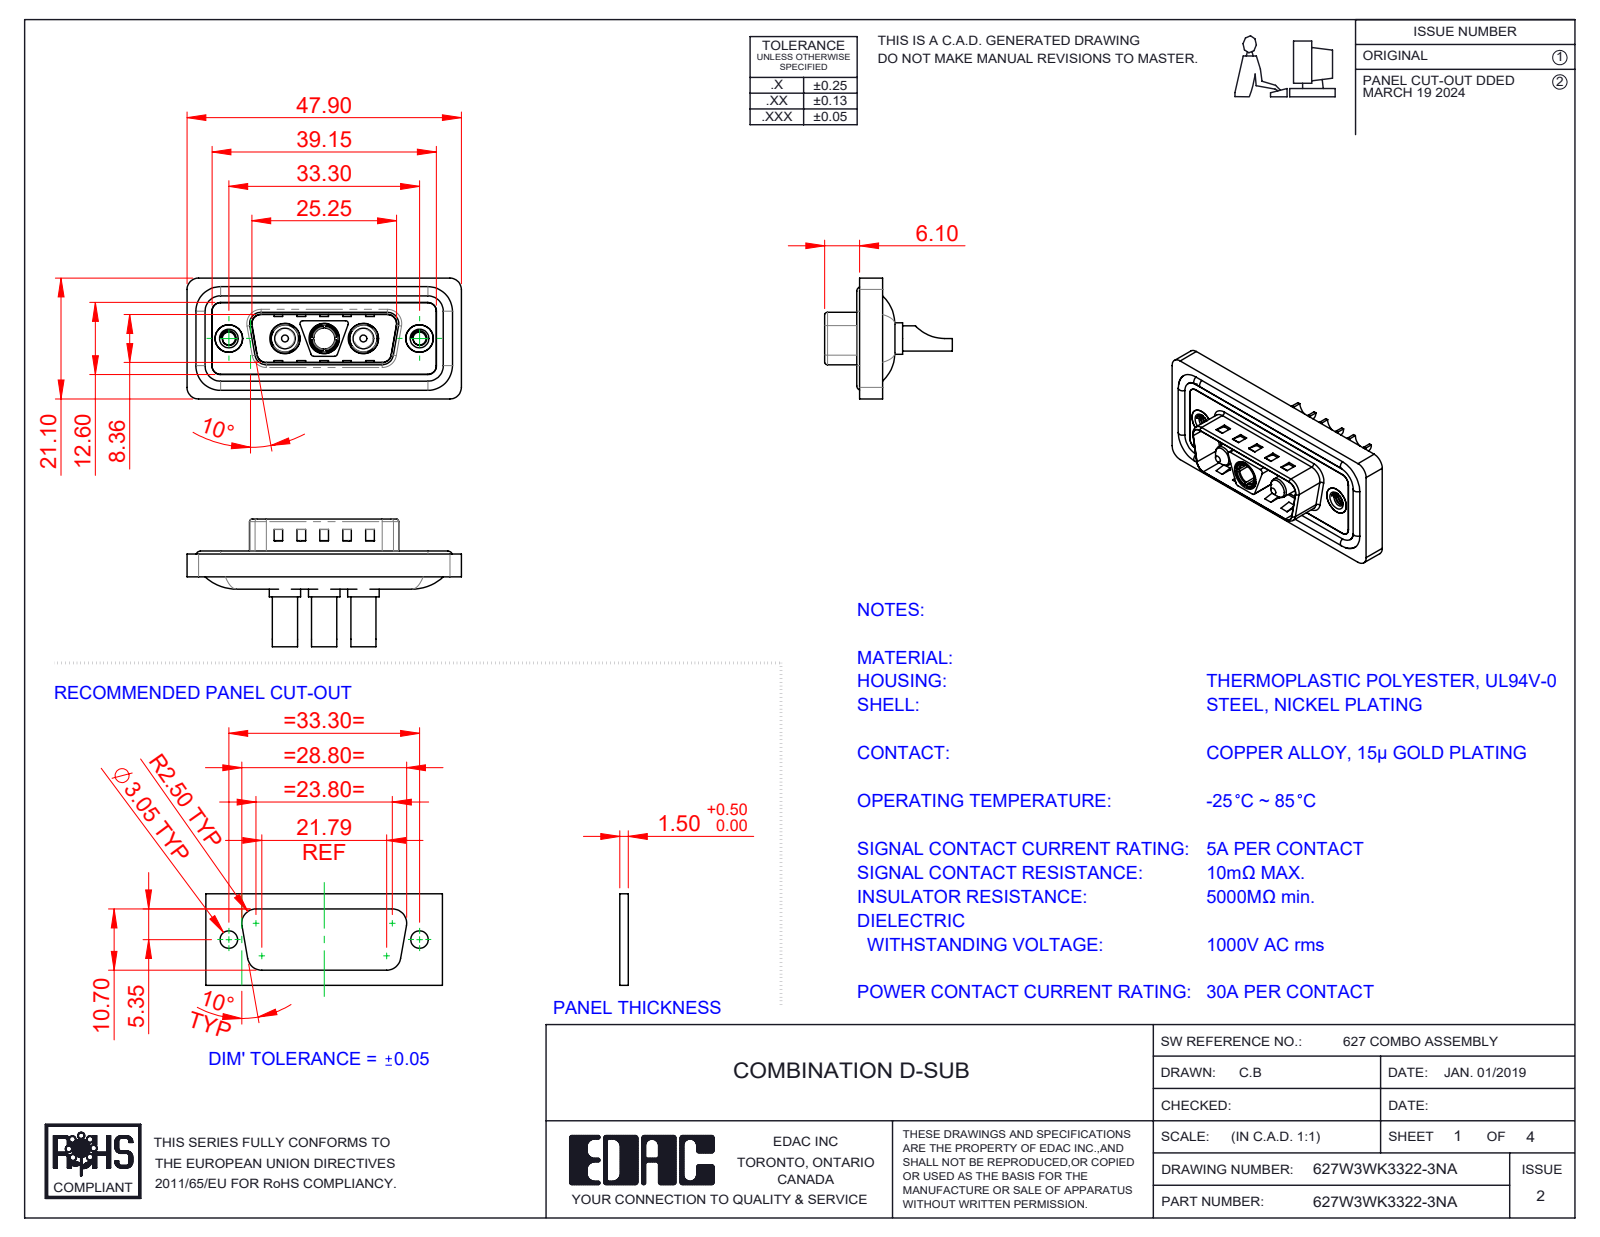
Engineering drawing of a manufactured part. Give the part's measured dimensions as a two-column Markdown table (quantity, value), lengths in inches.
| quantity | value |
| --- | --- |
| part name | Power Pin_30A SC; 627Combo Threaded Rivet_A; 627Combo Waterproof Housing_15 Contacts; Power Socket_30A SC (+4 more) |
| STEP written by | SolidWorks 2023 (CONFIG_CONTROL_DESIGN) |
| units | inches |
| bodies | 13 solids, 625 faces (240 planar, 261 cylindrical, 124 other) |
| overall size | 1.886 × 0.878 × 0.831 |
| volume | 0.352 in³ |
| surface area | 14.64 in² |
| round holes (diameter × count) | 0.138 × 3, 0.191 × 3, 0.209 × 3, 0.089 × 2, 0.157 × 2, 0.189 × 2, 0.197 × 2, 0.146 × 1 |
| round bosses / shafts (diameter × count) | 0.063 × 4, 0.217 × 3, 0.205 × 3, 0.187 × 3, 0.173 × 3, 0.148 × 3, 0.193 × 2, 0.142 × 2 |
| partial cylindrical surfaces (radius × count) | 0.059 × 26, 0.079 × 20, 0.02 × 12, 0.063 × 8, 0.01 × 4, 0.024 × 4, 0.026 × 4, 0.035 × 4 |
| main face-to-face distances | 0.016, 0.043, 0.02, 0.063, 0.122, 0.059, 0.114, 0.032, 0.377, 0.098 |
| hole center spacings | 0.27, 0.386, 0.656, 0.925, 0.539, 1.311 |
